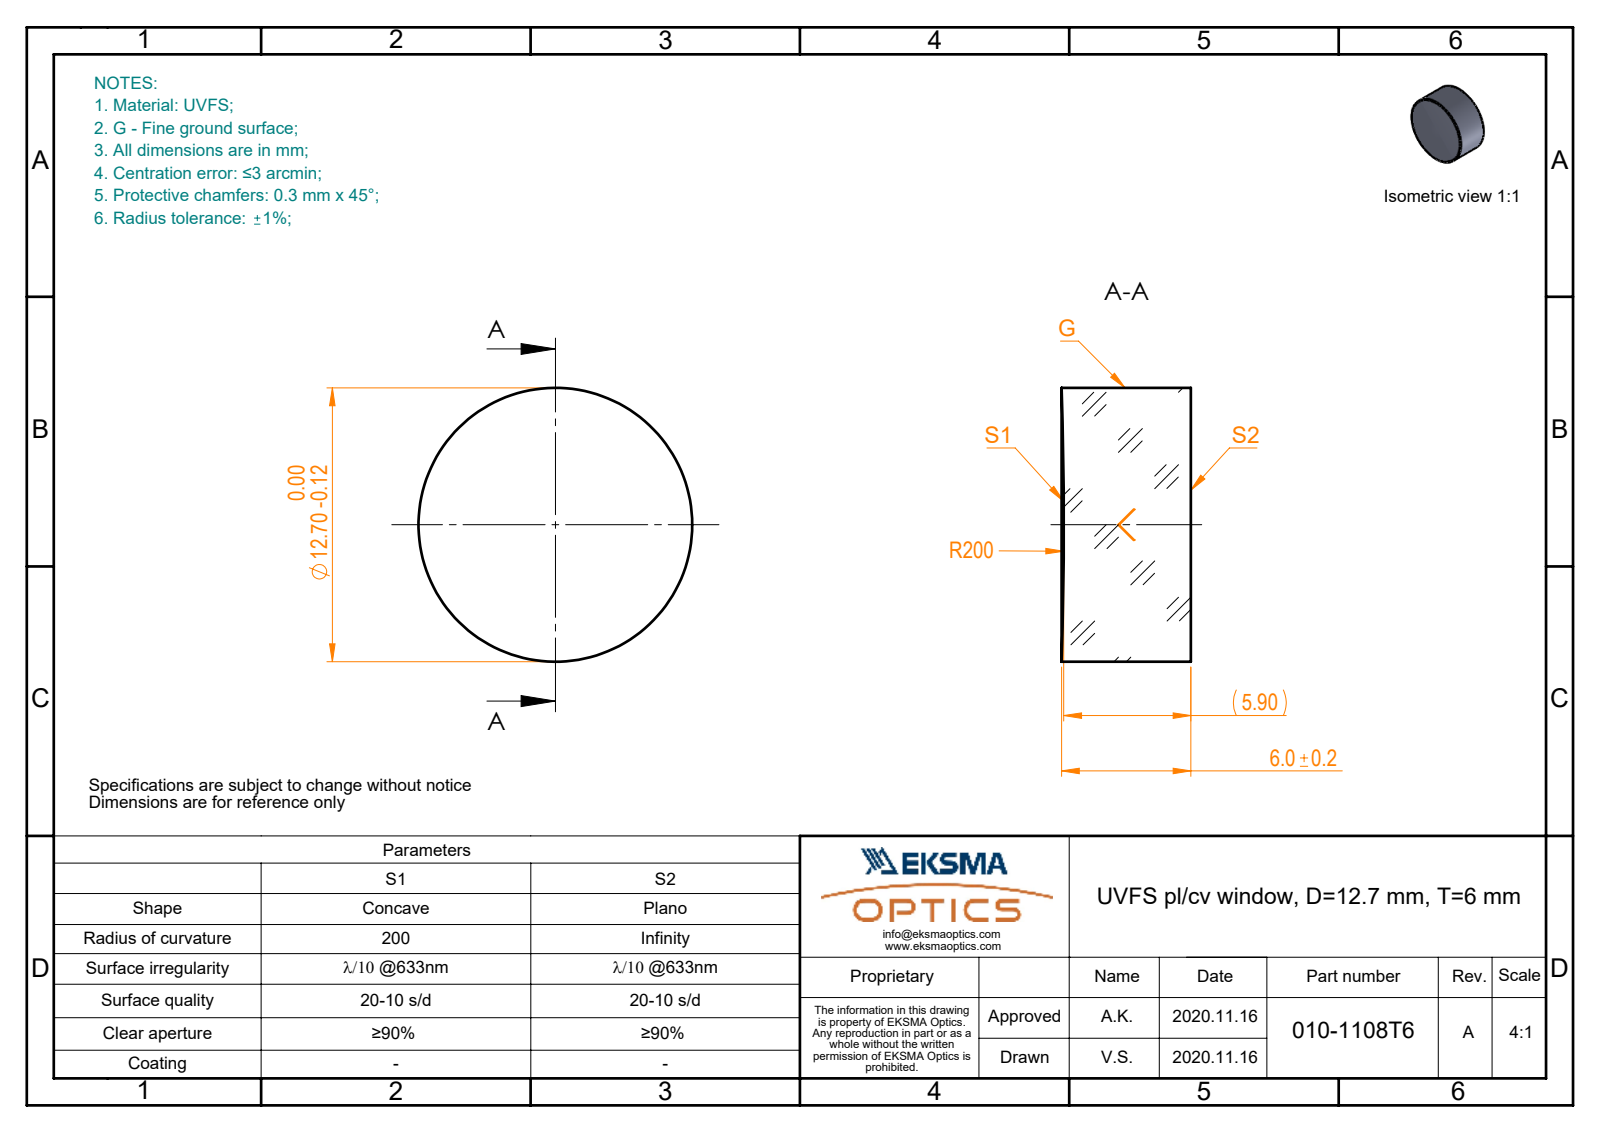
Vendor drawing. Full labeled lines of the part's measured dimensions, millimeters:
Part name (STEP PRODUCT): 010-1108T6_UVFS_PCV_window
STEP written by: SolidWorks 2019 (CONFIG_CONTROL_DESIGN)
Units: millimetres
Bodies: 1 solid, 5 faces (1 planar, 2 cylindrical, 2 other)
Overall size (bounding box): 12.7 × 12.7 × 6
Volume: 754 mm³ · Surface area: 493 mm²
Round bosses / shafts (diameter × count): ⌀12.7 ×1
